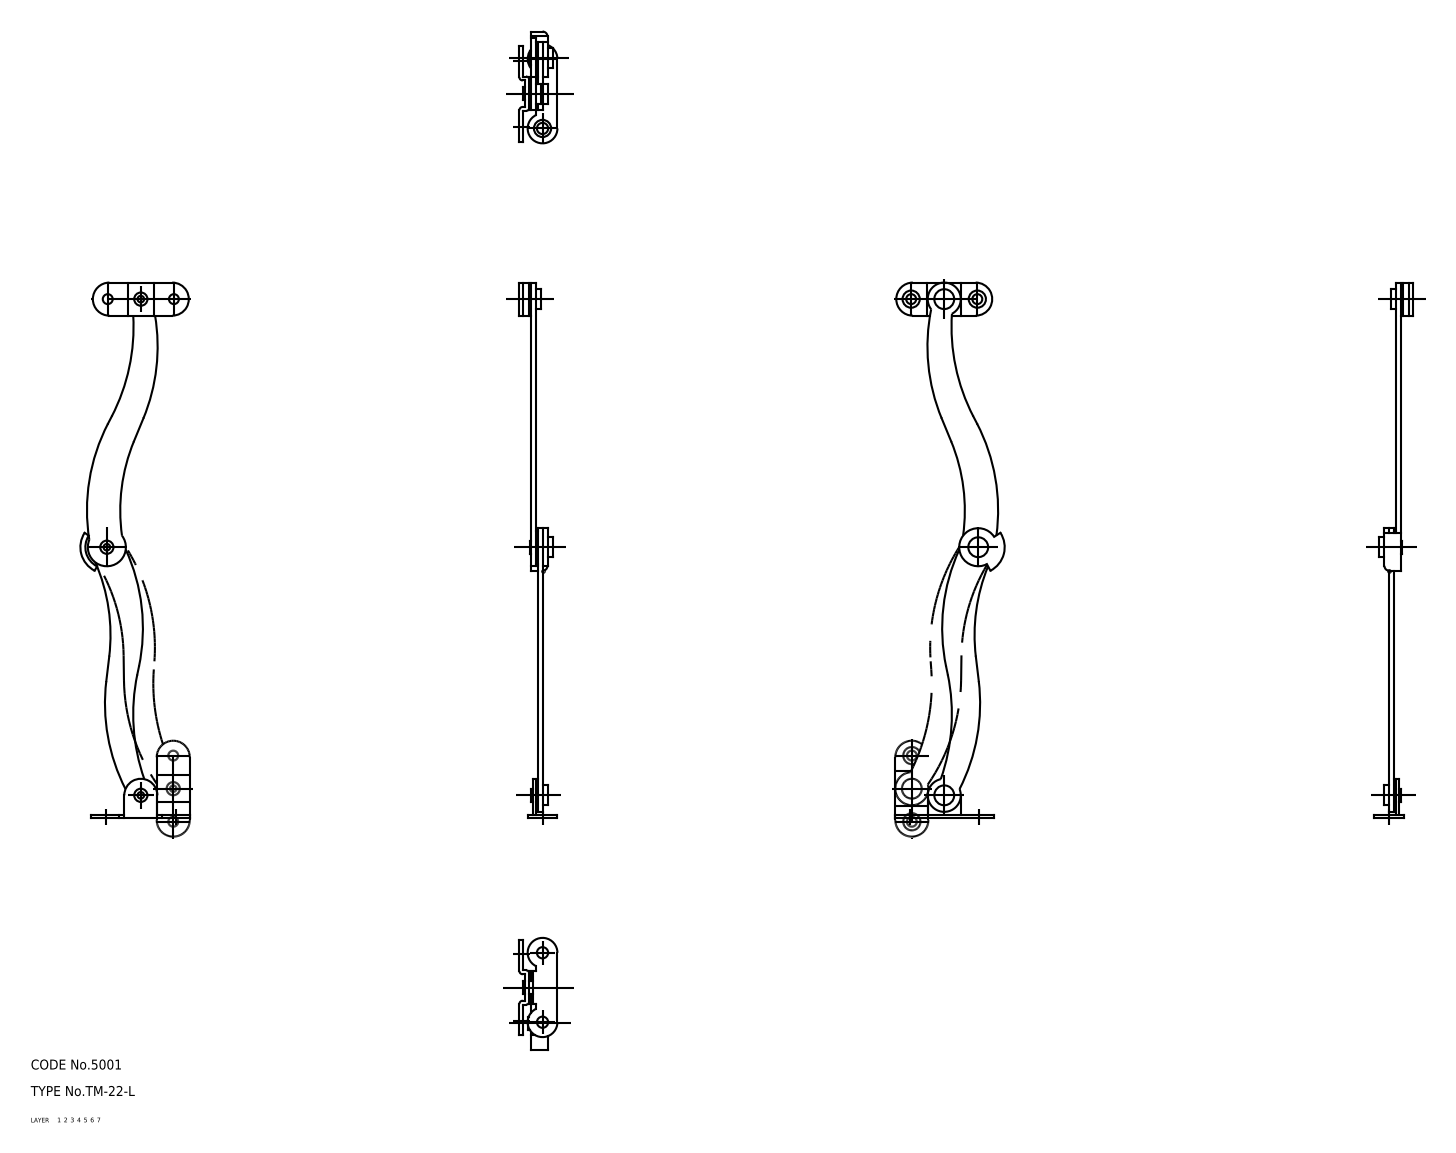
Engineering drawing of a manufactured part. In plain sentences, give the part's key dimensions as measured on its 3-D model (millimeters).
The part is named "rivet_3; rivet_1; rivet_2; washer (+5 more)". Its 3-D file was written by "CADfix (AUTOMOTIVE_DESIGN)". It is 11 solids with 138 faces: 0 planar, 0 cylindrical and 138 other. Overall it measures 162 by 33.27 by 11.5 millimeters. Its volume is 3 499 cubic millimeters and its surface area 6 402 square millimeters.
